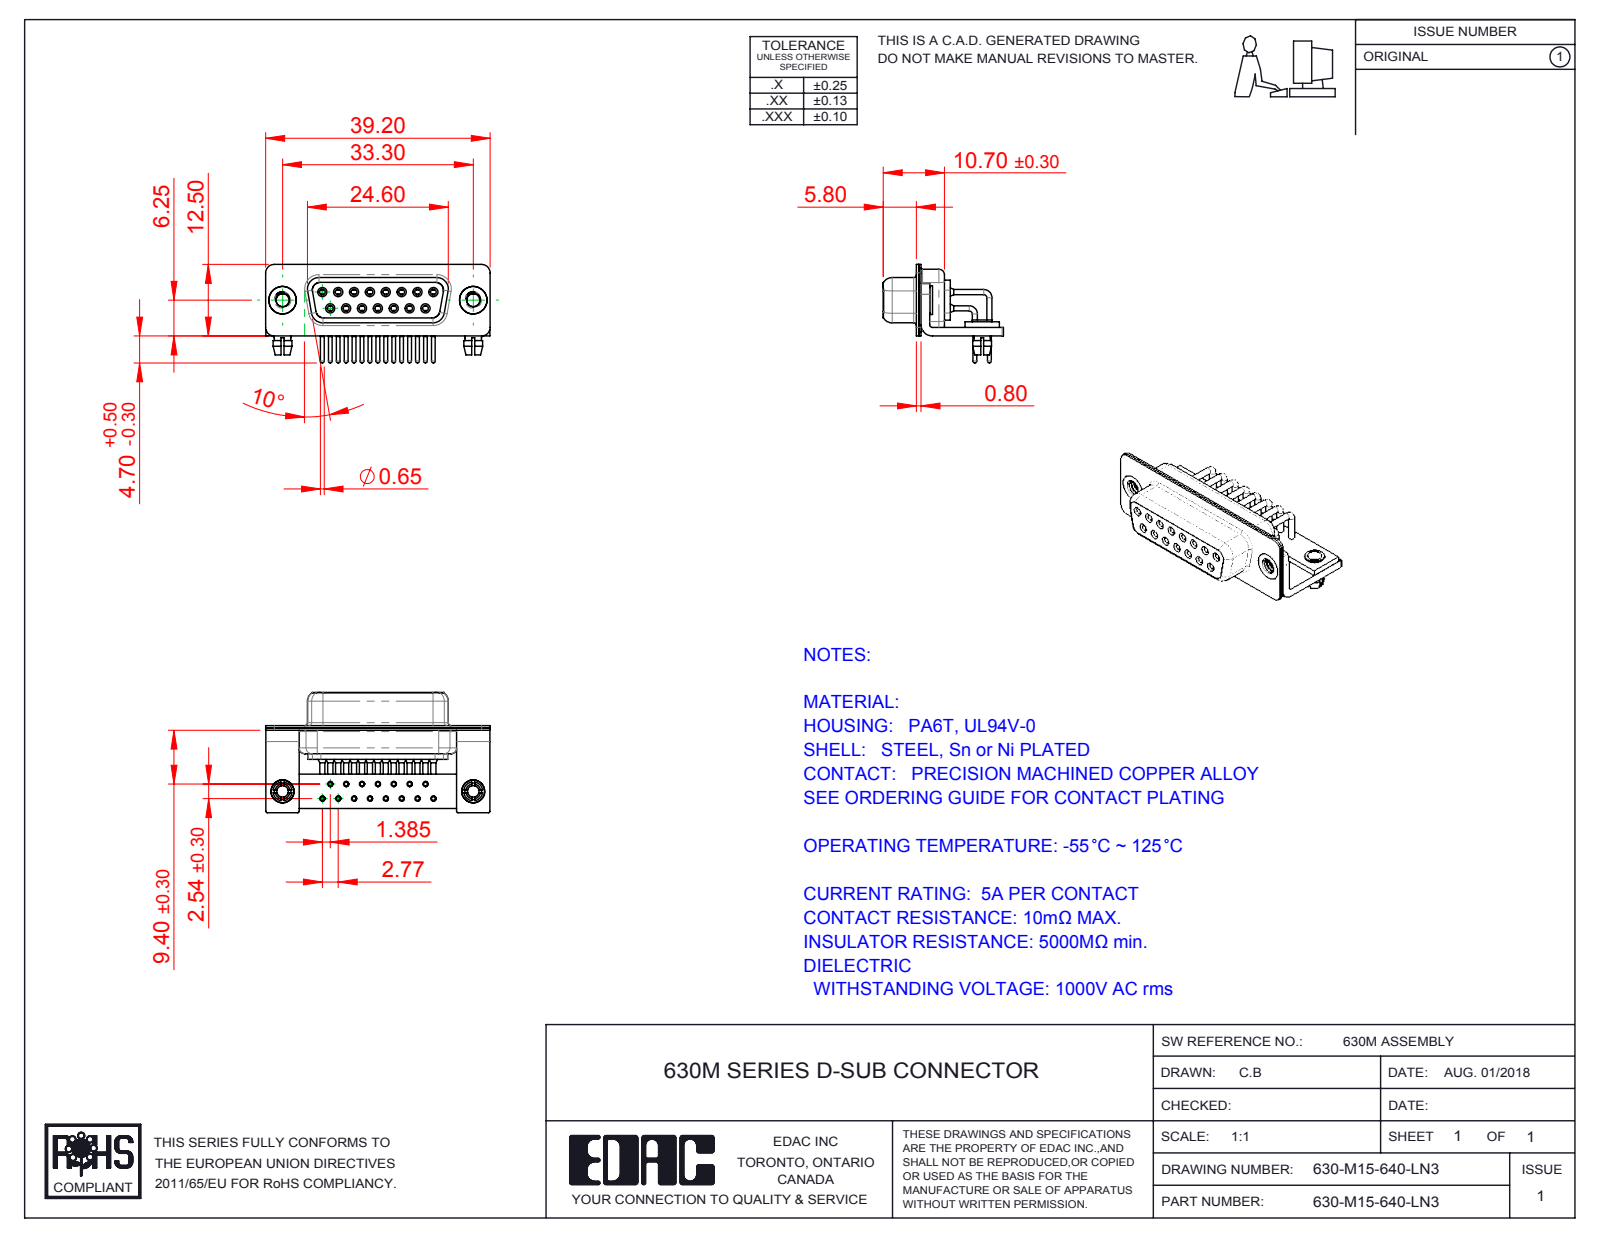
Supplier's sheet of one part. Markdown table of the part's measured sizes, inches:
| quantity | value |
| --- | --- |
| part name | 630M Housing_15 Contacts; 630-M15-640-LN3; 630M Stabilizer Board_15 Contacts; 630M Stabilizer Bracket (+6 more) |
| STEP written by | SolidWorks 2016 (CONFIG_CONTROL_DESIGN) |
| units | inches |
| bodies | 25 solids, 1246 faces (366 planar, 566 cylindrical, 314 other) |
| overall size | 1.543 × 0.827 × 0.677 |
| volume | 0.189 in³ |
| surface area | 12.33 in² |
| round holes (diameter × count) | 0.079 × 17, 0.035 × 15, 0.039 × 15, 0.043 × 15, 0.067 × 15, 0.071 × 15, 0.089 × 2, 0.098 × 2, 0.126 × 2, 0.157 × 2, 0.189 × 2 |
| round bosses / shafts (diameter × count) | 0.035 × 27, 0.063 × 15, 0.059 × 15, 0.026 × 15, 0.197 × 2, 0.193 × 2, 0.157 × 2, 0.134 × 2 |
| partial cylindrical surfaces (radius × count) | 0.01 × 16, 0.059 × 16, 0.079 × 13, 0.053 × 8, 0.063 × 8, 0.02 × 5, 0.024 × 4, 0.026 × 4 |
| main face-to-face distances | 0.016, 0.031, 0.091, 0.059, 0.368, 0.075, 0.039, 0.057, 0.352, 0.033 |
| hole center spacings | 0.109, 0.218, 0.327, 0.124, 0.192, 0.436, 0.114, 0.29 |
